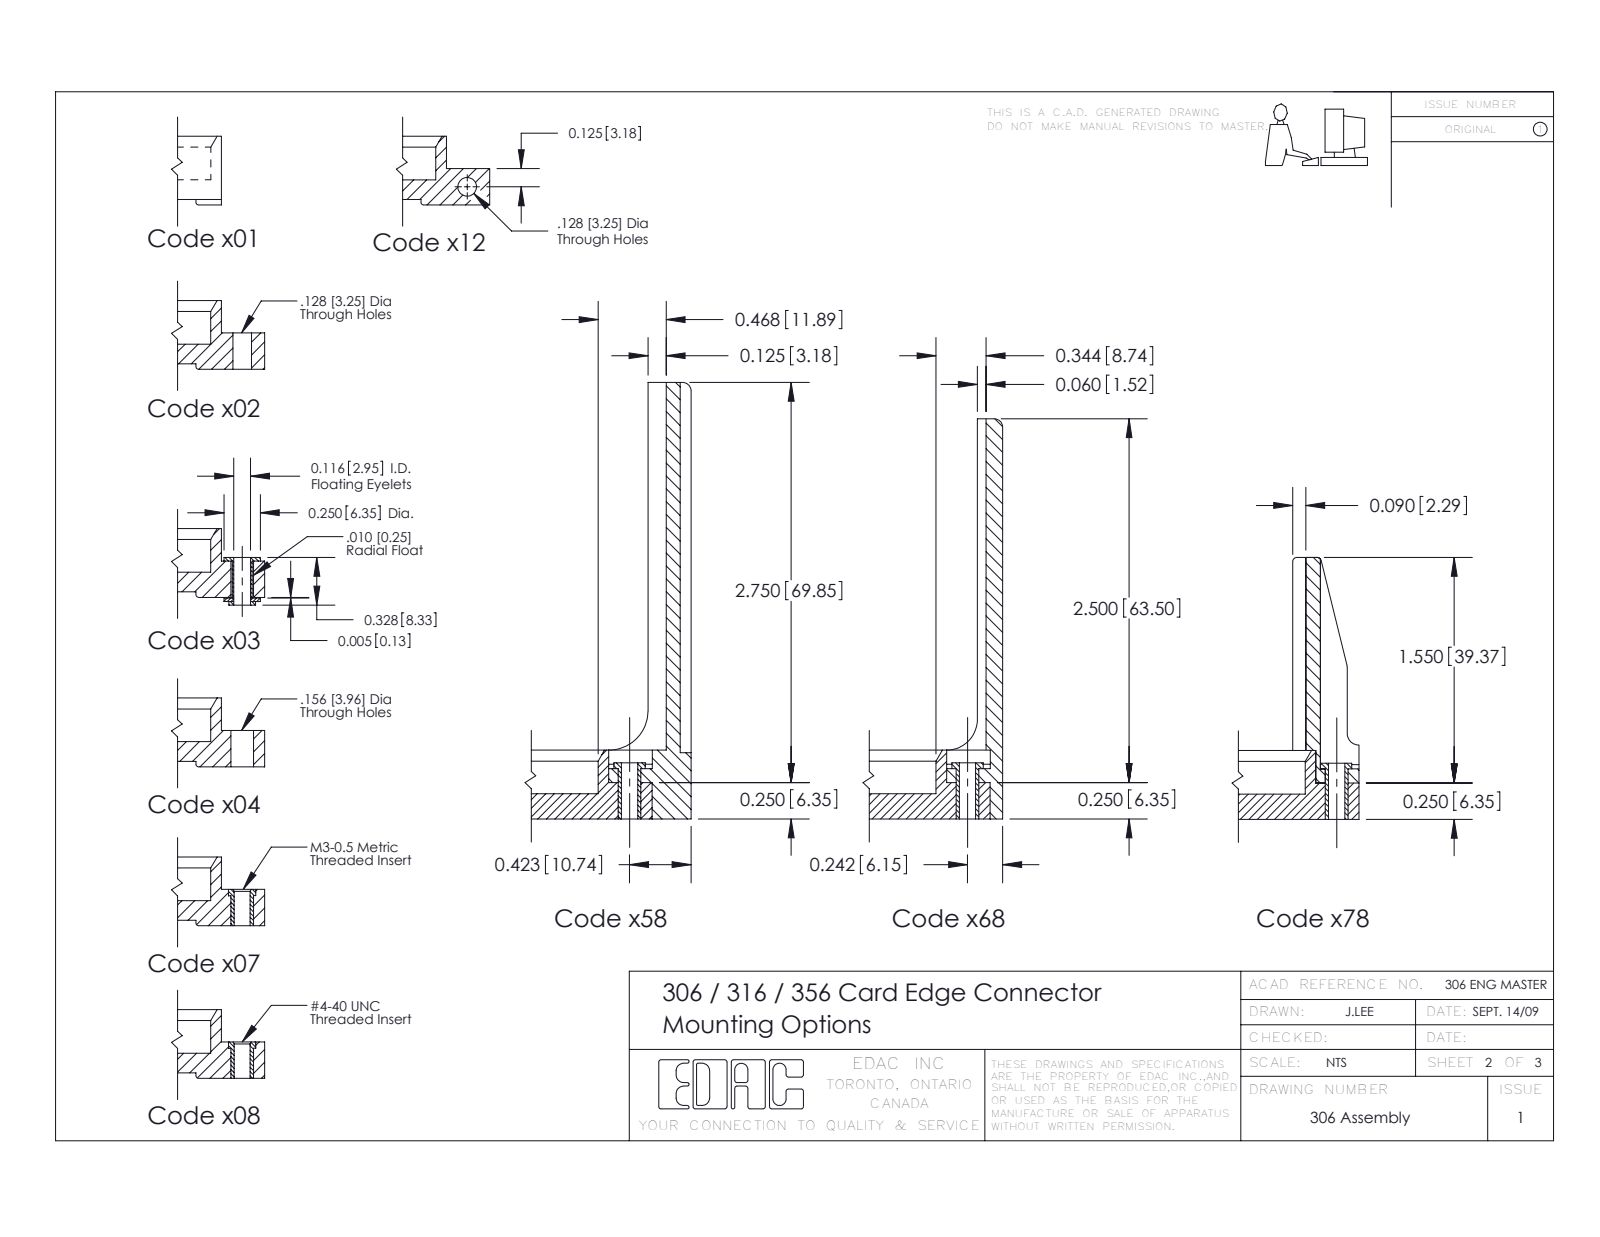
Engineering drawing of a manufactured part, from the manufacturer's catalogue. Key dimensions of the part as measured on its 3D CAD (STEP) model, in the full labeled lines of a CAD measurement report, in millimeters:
Part name (STEP PRODUCT): 306-290-001_121; 306 Part_.128 Dia; 316-011-521-102
STEP written by: SolidWorks 2016 (CONFIG_CONTROL_DESIGN)
Units: millimetres
Bodies: 12 solids, 886 faces (585 planar, 257 cylindrical, 44 other)
Overall size (bounding box): 66.6 × 14.9 × 8.7
Volume: 4 460 mm³ · Surface area: 5 899 mm²
Round holes (diameter × count): ⌀3.3 ×2
Partial cylindrical surfaces — rounded edges, fillets, slot ends (radius × count): R0.4 ×38, R0.3 ×22, R0.5 ×11, R0.2 ×6, R0.8 ×6, R0.7 ×3, R1.7 ×2, R2.1 ×2
Main face-to-face distances: 8.7, 2.1, 6.6, 0.4, 4, 4.6, 10.9, 1.2, 9.7, 15.8
Hole centre spacings: 58.7
